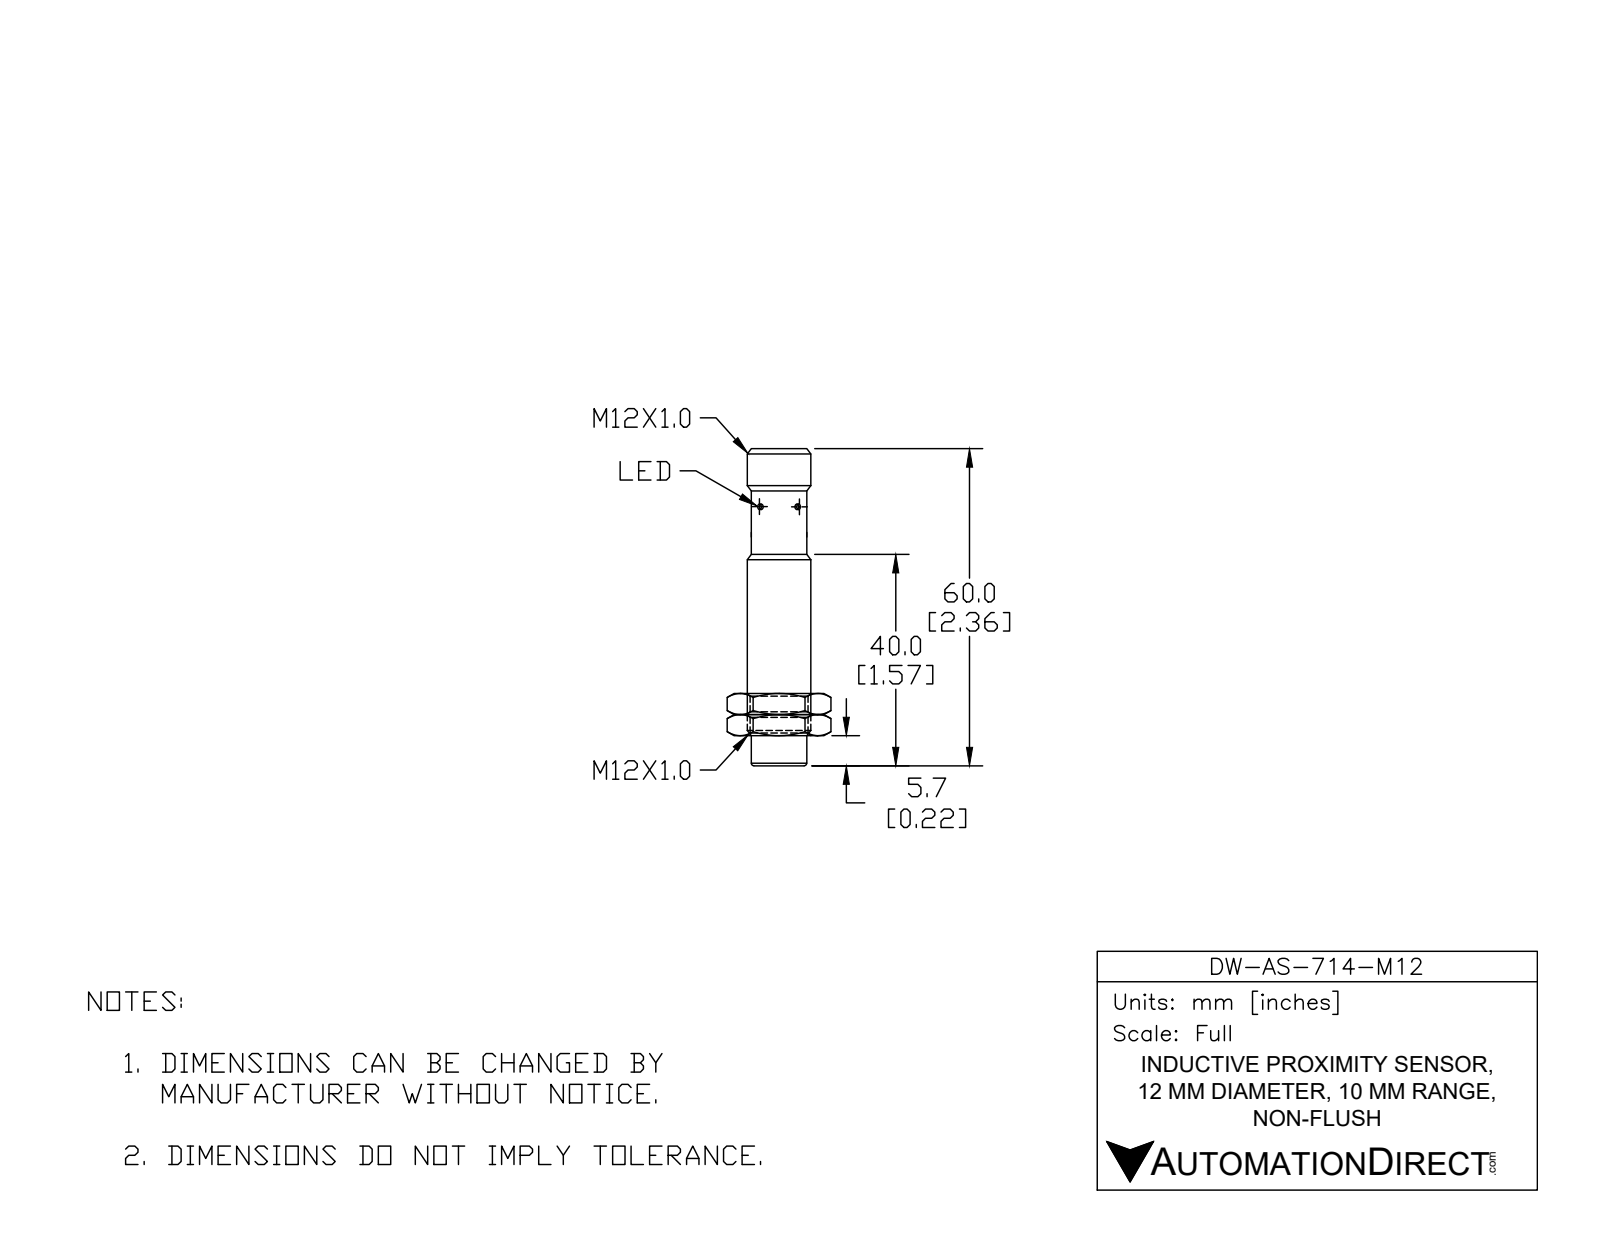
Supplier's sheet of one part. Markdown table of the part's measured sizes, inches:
| quantity | value |
| --- | --- |
| part name | DW-AS-714-M12 |
| STEP written by | SolidWorks 2017 (AUTOMOTIVE_DESIGN) |
| units | inches |
| bodies | 1 solid, 40 faces (9 planar, 20 cylindrical, 11 other) |
| overall size | 2.362 × 0.472 × 0.472 |
| volume | 0.359 in³ |
| surface area | 4.295 in² |
| round holes (diameter × count) | 0.118 × 2, 0.335 × 1 |
| round bosses / shafts (diameter × count) | 0.04 × 4, 0.472 × 1, 0.415 × 1 |
| partial cylindrical surfaces (radius × count) | 0.02 × 1, 0.02 × 1, 0.193 × 1 |
| main face-to-face distances | 2.02, 2.362, 0.343, 1.614, 0.406, 0.748, 2.047, 0.433, 0.028, 0.315 |
